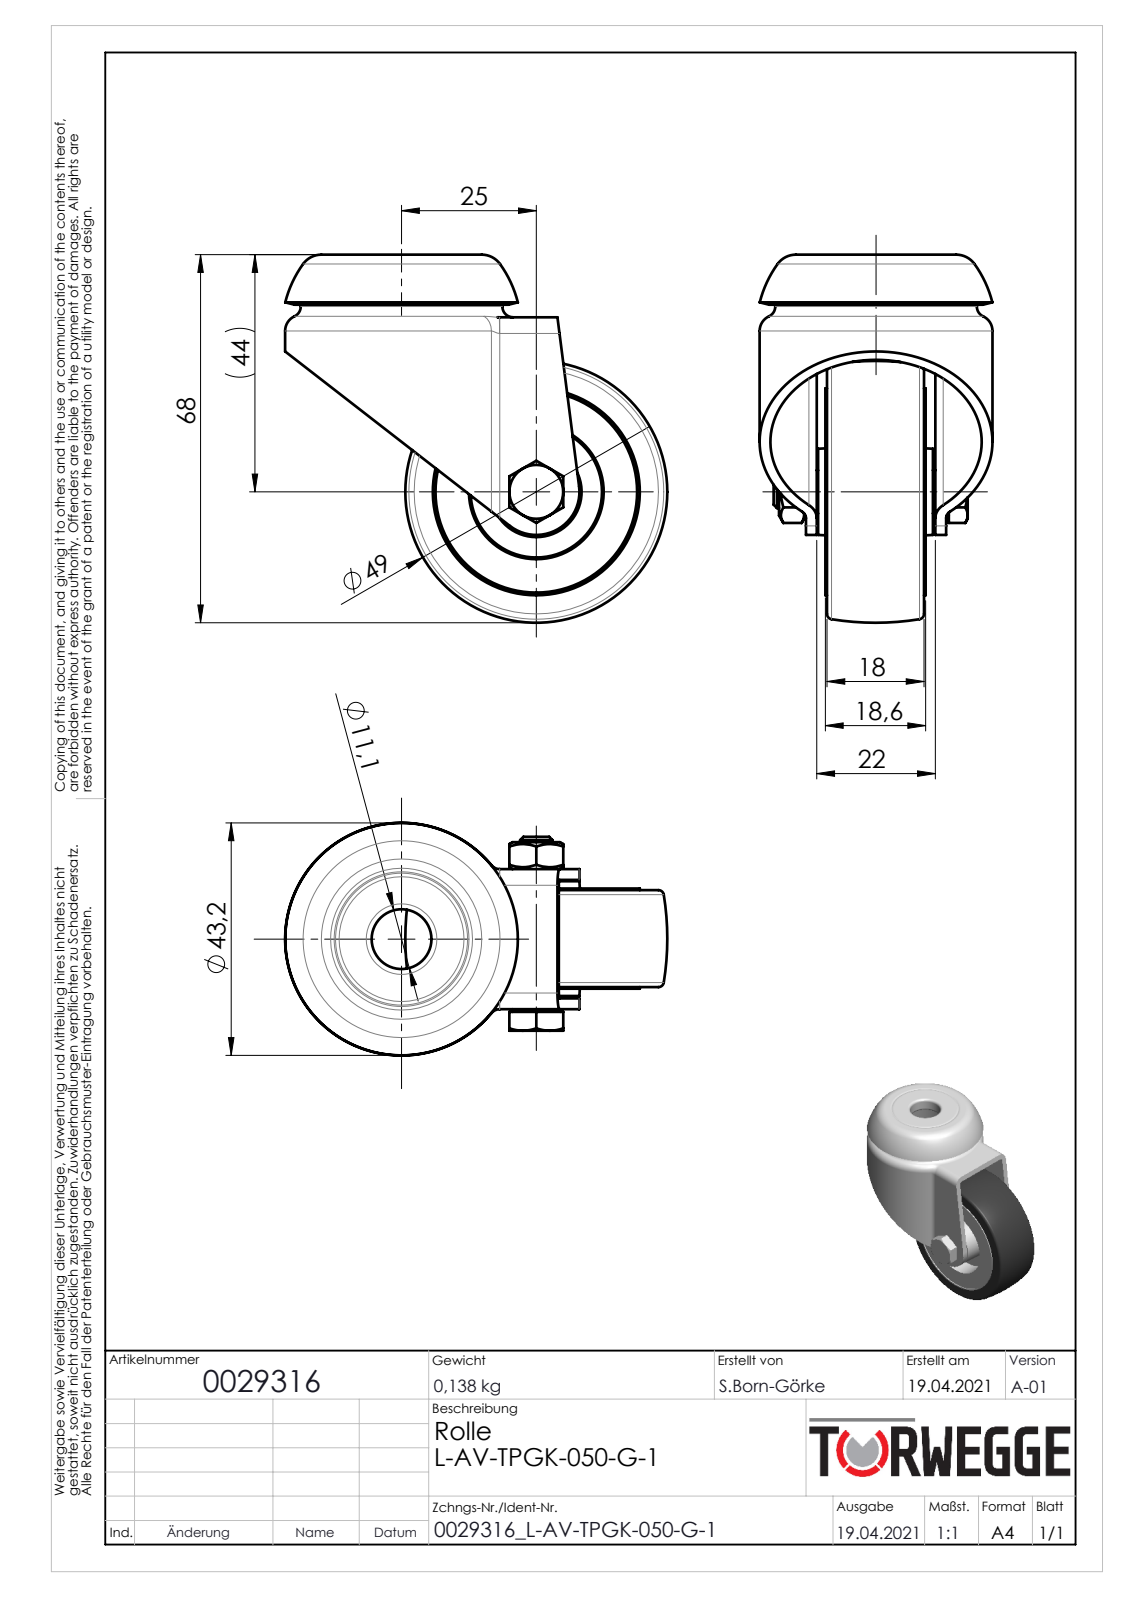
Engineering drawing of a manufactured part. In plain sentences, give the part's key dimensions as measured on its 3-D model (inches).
The part is named "0029316". Its 3-D file was written by "SolidWorks 2020 (AUTOMOTIVE_DESIGN)". It is 31 solids with 252 faces: 50 planar, 60 cylindrical and 142 other. Overall it measures 2.791 by 2.69 by 1.701 inches. Its volume is 2.849 cubic inches and its surface area 51.14 square inches. Round holes: 1 of diameter 0.194, 1 of diameter 0.24, 1 of diameter 0.244, 1 of diameter 0.319, 1 of diameter 0.437, 1 of diameter 0.551, 1 of diameter 1.063, 1 of diameter 1.299, 1 of diameter 1.315, 1 of diameter 1.472. Round bosses or shafts: 1 of diameter 1.512, 1 of diameter 1.472, 1 of diameter 1.304, 1 of diameter 1.142, 1 of diameter 0.616, 1 of diameter 0.537, 1 of diameter 0.35, 1 of diameter 0.315. Partial cylindrical surfaces (rounded edges, fillets, slot ends): 2 of radius 0.039, 2 of radius 0.079, 2 of radius 0.118, 2 of radius 0.157, 1 of radius 0.315, 1 of radius 0.772, 1 of radius 0.85. The main face-to-face distances are 0.079, 0.709, 0.945, 0.236, 0.071, 0.791, 0.862, 0.472, 0.87, 0.161.
